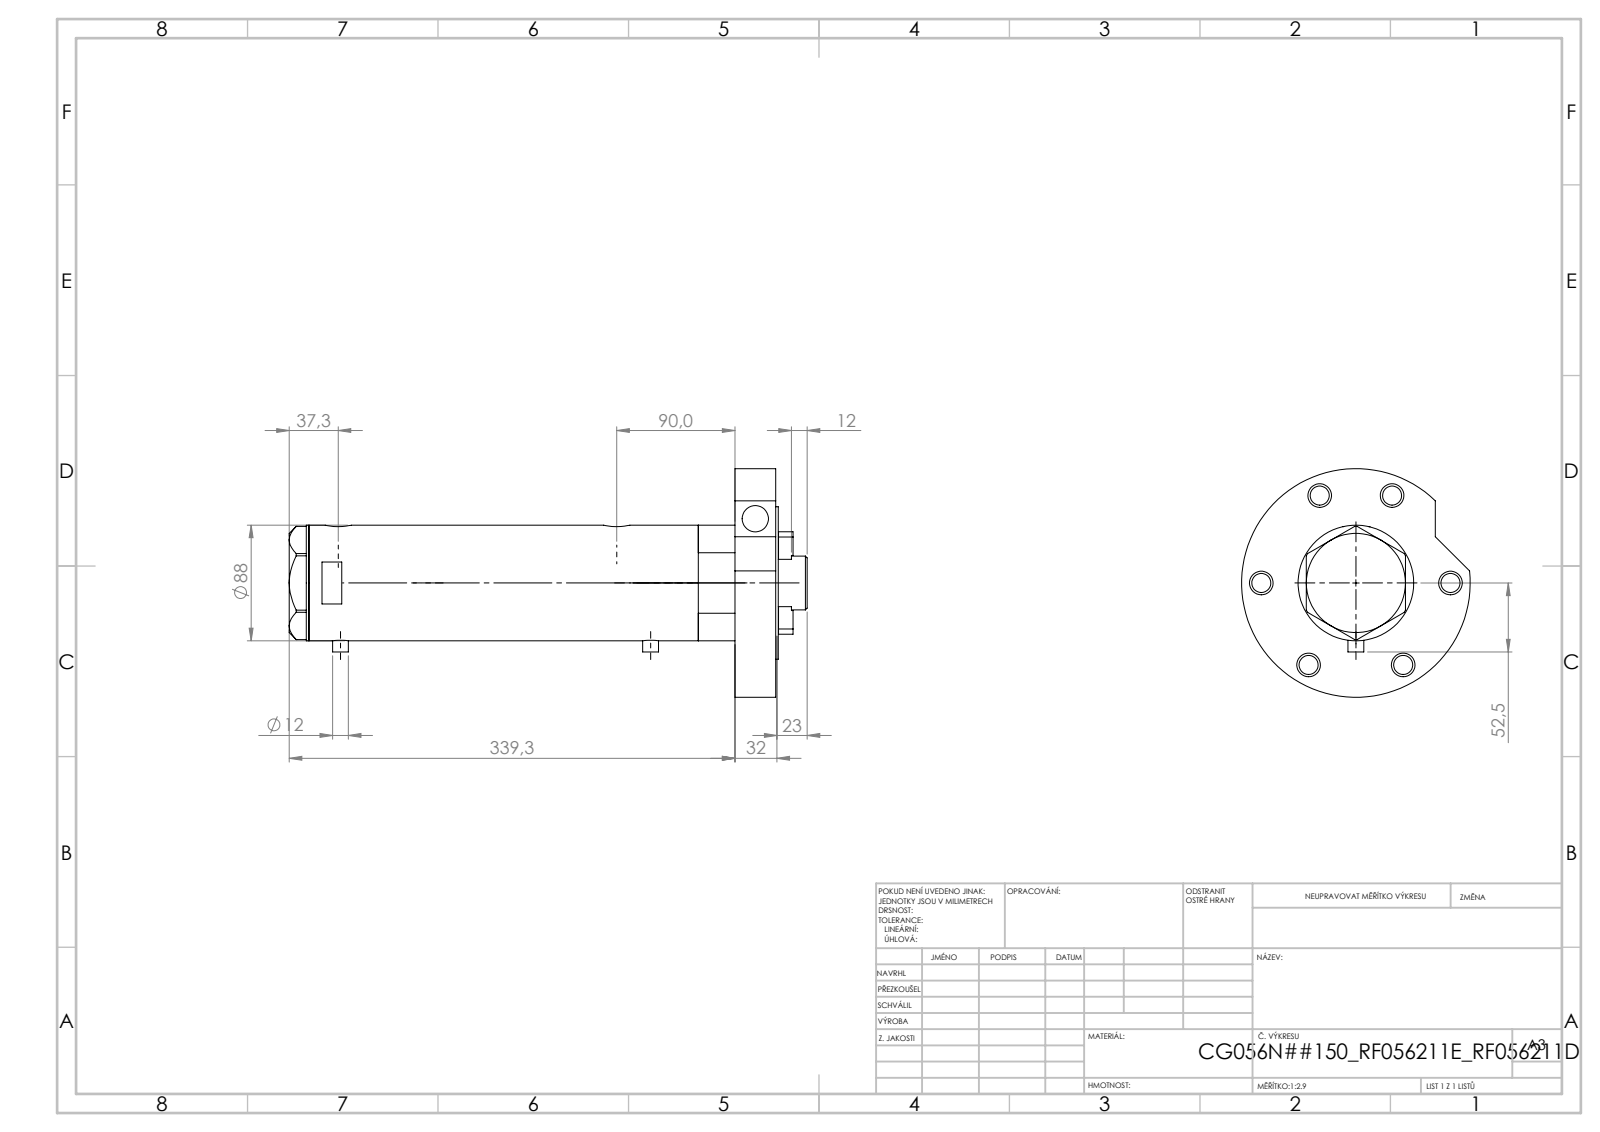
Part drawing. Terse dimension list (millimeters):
name: V270CG_RF211E; V270CG_BACK; V270CG_FRONT; V270CG_RF211D (+2 more)
written by: SolidWorks 2019 (CONFIG_CONTROL_DESIGN)
unit: mm
bodies: 7 solids, 205 faces (87 planar, 98 cylindrical, 20 other)
size: 394.3 × 174 × 174
volume: 2 564 000 mm³; area: 364 171 mm²
holes: 7× ⌀14.5, 6× ⌀18, 4× ⌀8.1, 4× ⌀13.5, 3× ⌀20, 2× ⌀12.5, 2× ⌀13.16, 1× ⌀42, 1× ⌀43.5, 1× ⌀56, 1× ⌀60, 1× ⌀75
bosses: 2× ⌀12, 1× ⌀174, 1× ⌀116, 1× ⌀88, 1× ⌀73, 1× ⌀41
face distances: 31, 357.3, 2, 324.3, 355.3, 33, 234.4, 89.9, 120.9, 122.9
hole spacings: 72, 30.35, 69.35, 86.03, 18, 41.87, 42.93, 52.39
